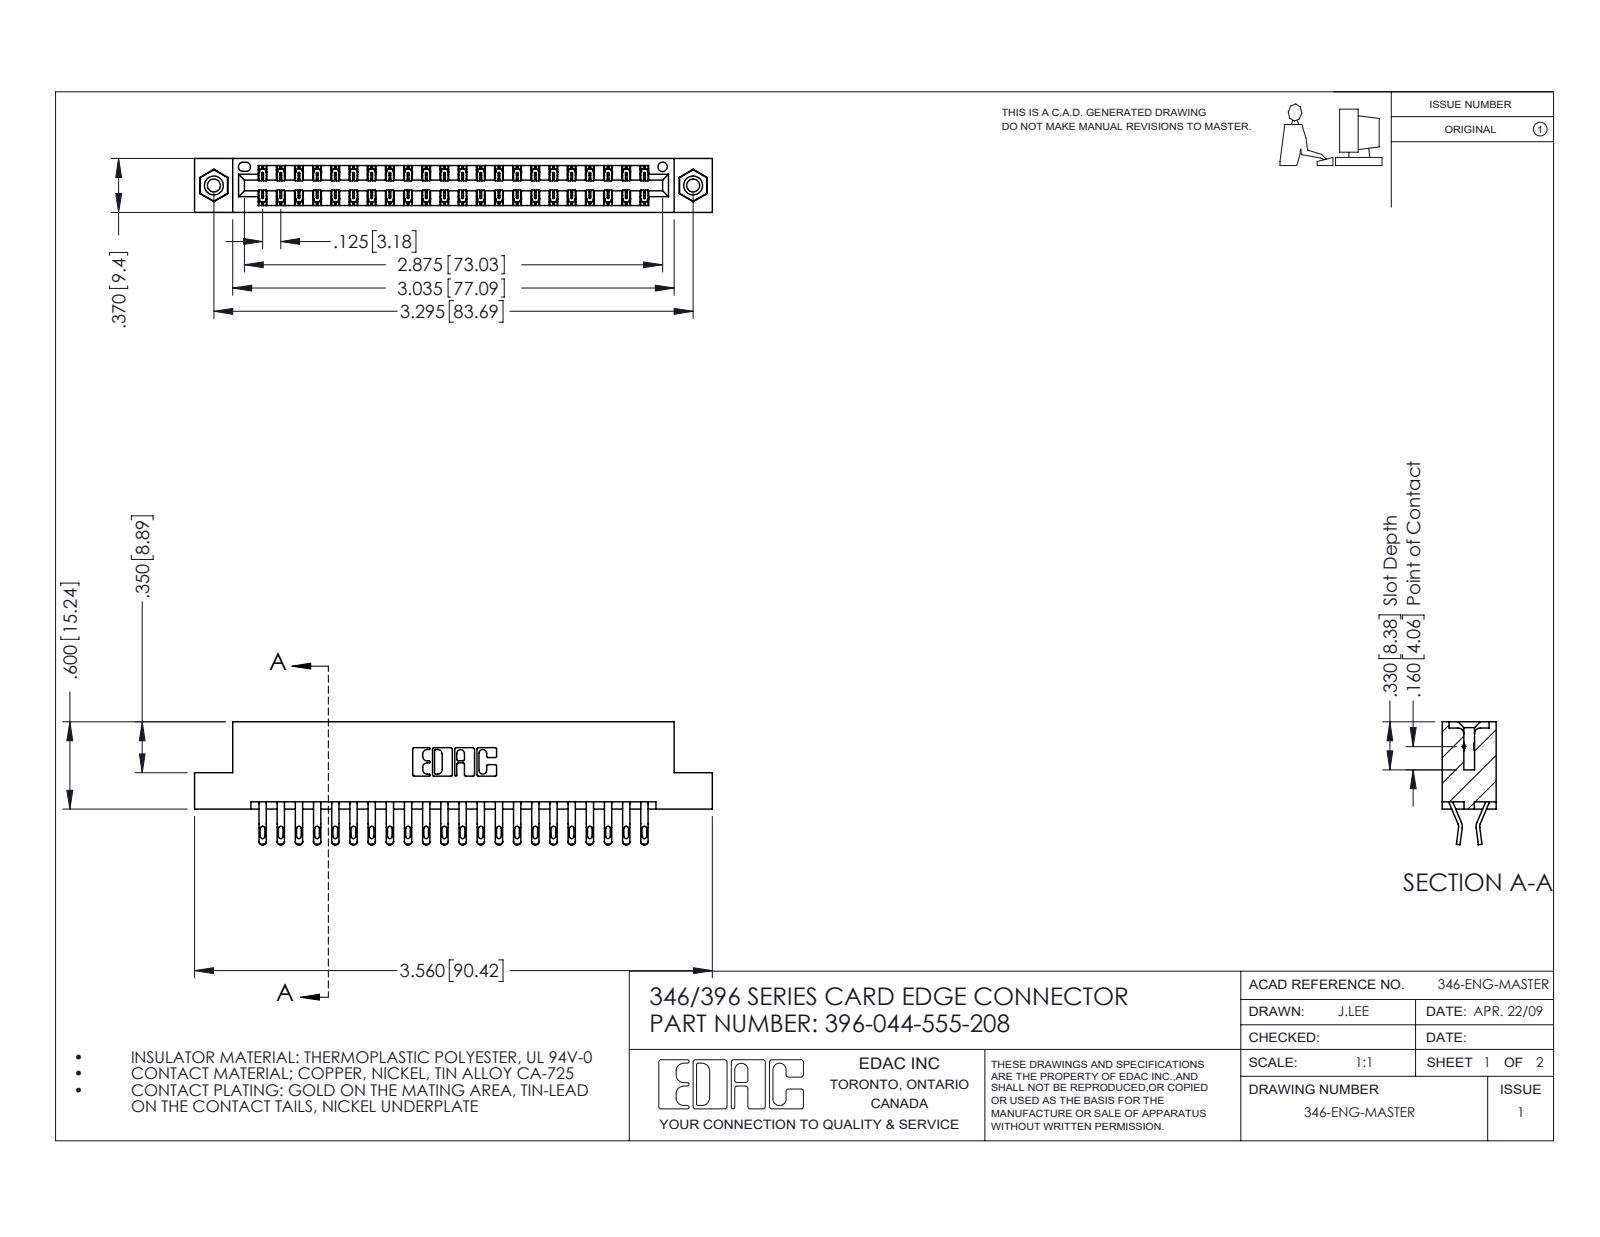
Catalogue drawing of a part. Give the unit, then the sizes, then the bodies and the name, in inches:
Units: inches
Overall size (bounding box): 3.56 × 0.845 × 0.37
Round holes (diameter × count): ⌀0.089 ×2, ⌀0.125 ×2, ⌀0.156 ×2, ⌀0.064 ×1
Round bosses / shafts (diameter × count): ⌀0.155 ×2
Partial cylindrical surfaces — rounded edges, fillets, slot ends (radius × count): R0.016 ×88, R0.02 ×88, R0.006 ×66, R0.01 ×22, R0.007 ×6, R0.031 ×6, R0.026 ×3, R0.01 ×2
Main face-to-face distances: 0.048, 0.322, 0.25, 0.37, 0.025, 0.072, 0.298, 0.275, 0.148, 0.222
Hole centre spacings: 0.246, 3.087, 3.295
Volume: 0.536 in³ · Surface area: 18.96 in²
Bodies: 47 solids, 2734 faces (1560 planar, 1158 cylindrical, 16 other)
Part name (STEP PRODUCT): 345-250-001_345-250-003-102; 345-292-001_555 Tail; 396-044-555-208; 346 Part_Flush Mounting Lugs - 0.156 Dia-TI
STEP written by: SolidWorks 2016 (CONFIG_CONTROL_DESIGN)
